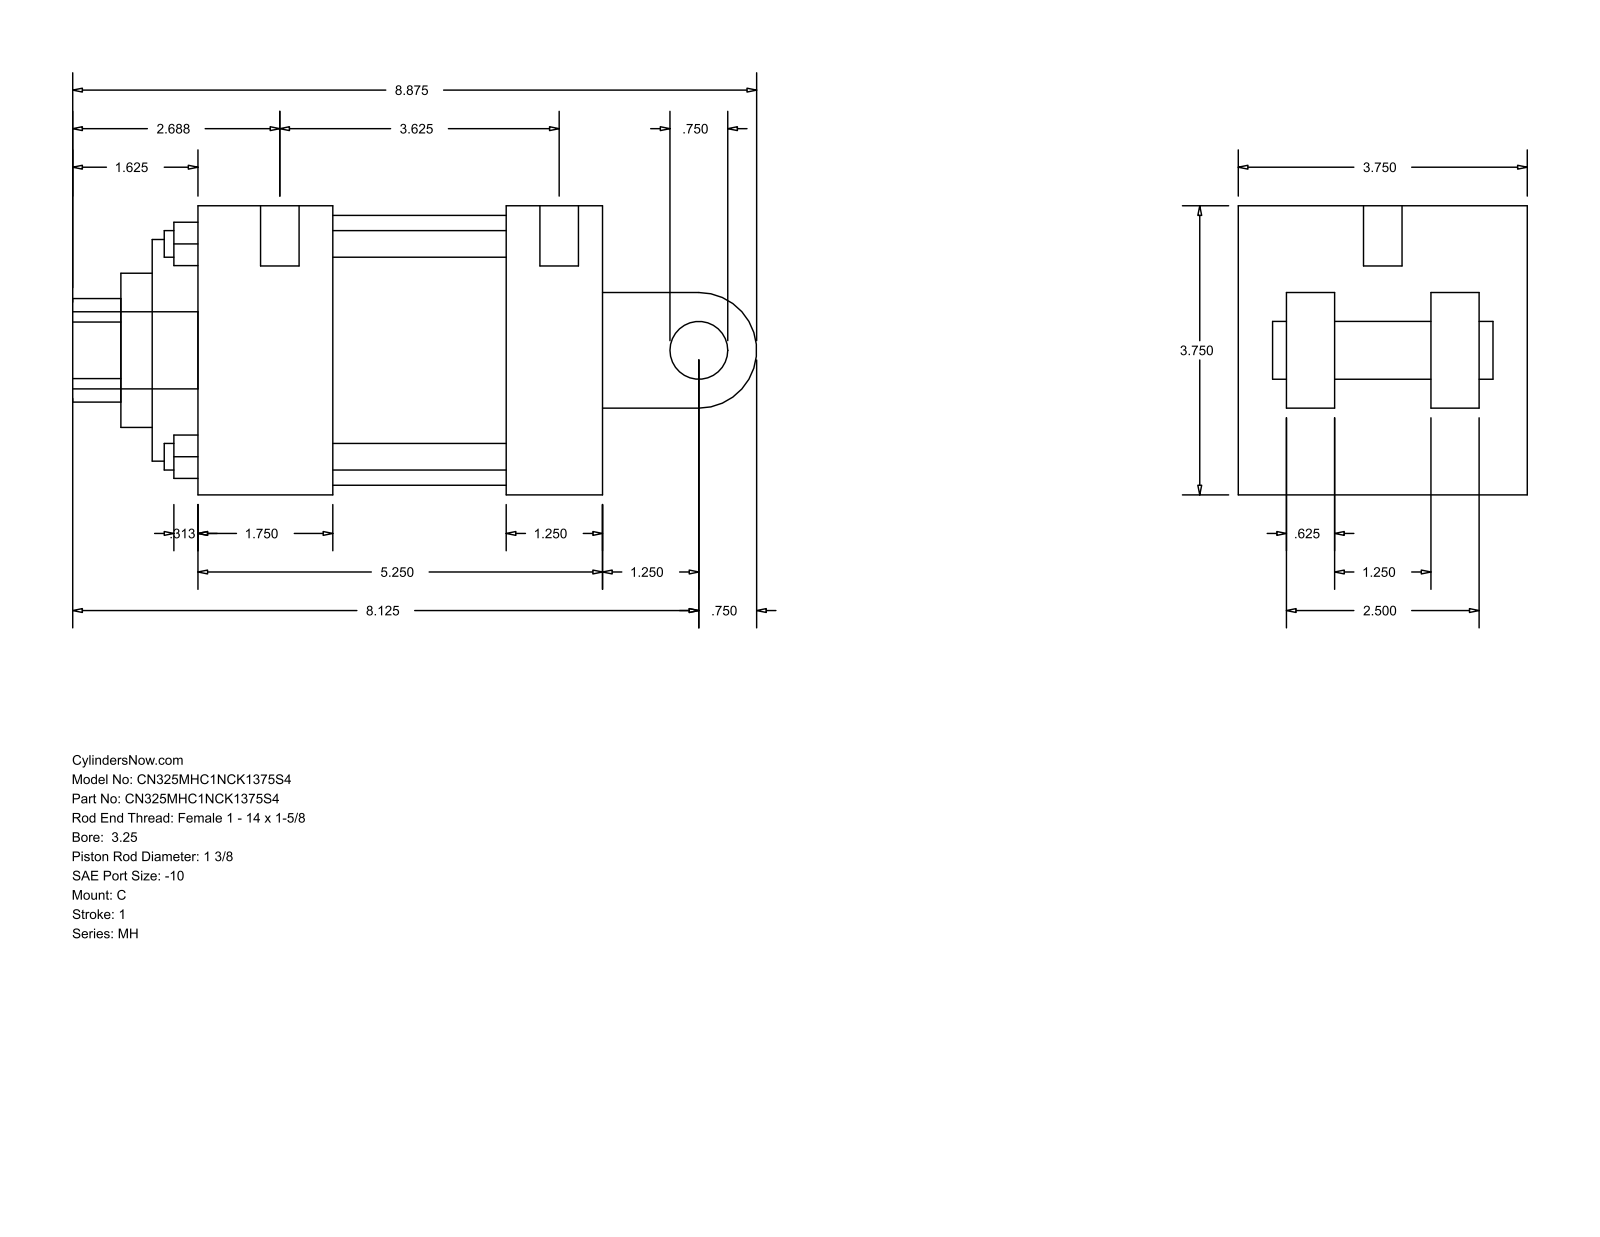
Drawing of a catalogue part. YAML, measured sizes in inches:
part_name: "MH_C__0325_1.375"
step_written_by: "GSSL Pune (CONFIG_CONTROL_DESIGN)"
units: inches
bodies: {solids: 0, faces: 101, planar: 71, cylindrical: 30, other: 0}
overall_size: [8.875, 3.75, 3.75]
round_holes:
  - {diameter: 0.345, count: 4}
  - {diameter: 0.219, count: 2}
  - {diameter: 0.5, count: 1}
  - {diameter: 1.375, count: 1}
  - {diameter: 2, count: 1}
  - {diameter: 2.875, count: 1}
  - {diameter: 3.5, count: 1}
round_bosses_or_shafts:
  - {diameter: 0.219, count: 2}
  - {diameter: 1, count: 1}
  - {diameter: 0.75, count: 1}
  - {diameter: 0.5, count: 1}
partial_cylinders:
  - {radius: 0.672, count: 1}
  - {radius: 0.75, count: 1}
face_to_face_distances: [3.75, 0.625, 1.25, 5.25, 2.5, 3.125, 1.875, 1.75, 4, 2.25]
hole_center_spacings: [1.952, 2.76, 3.903, 0.187]
